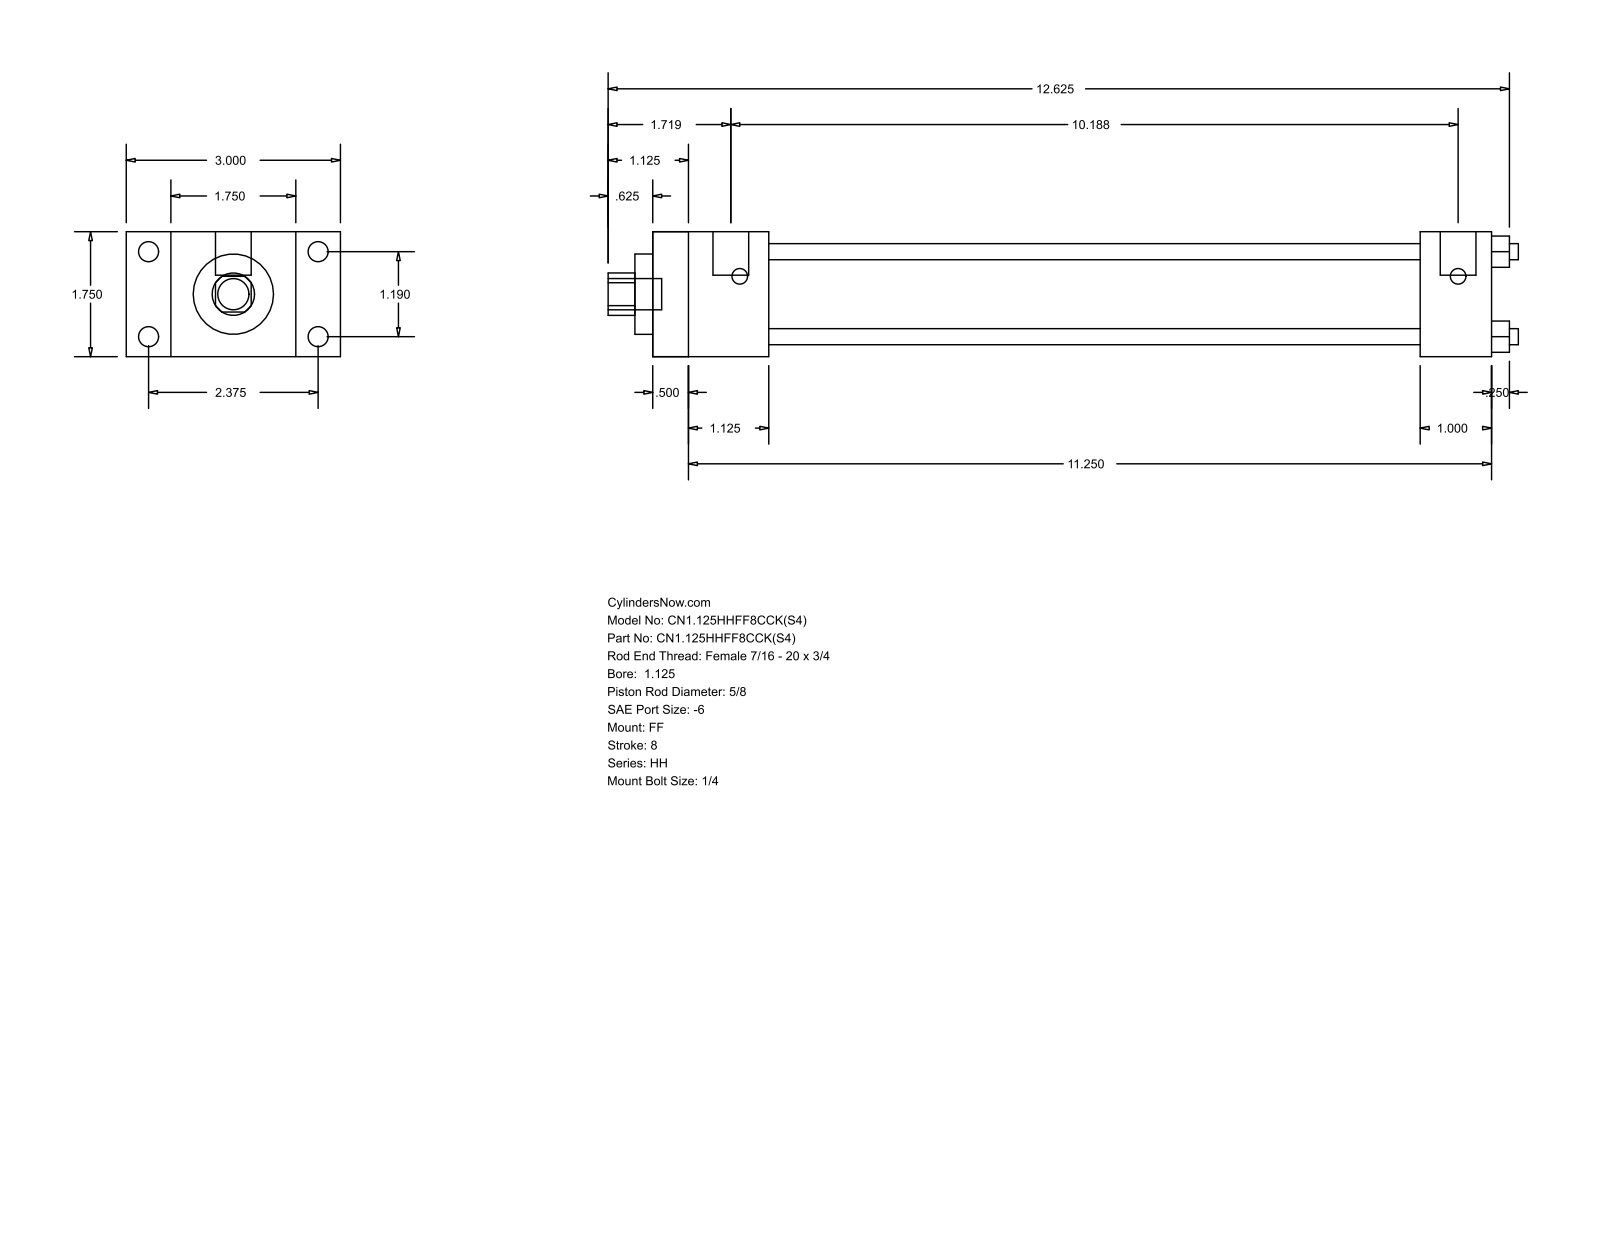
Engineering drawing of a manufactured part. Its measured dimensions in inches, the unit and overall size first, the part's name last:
Units: inches
Overall size (bounding box): 12.75 × 3 × 1.75
Round holes (diameter × count): ⌀0.225 ×4, ⌀0.625 ×1, ⌀1.125 ×1, ⌀1.375 ×1
Round bosses / shafts (diameter × count): ⌀0.281 ×4, ⌀0.219 ×4, ⌀0.5 ×2, ⌀0.437 ×1
Partial cylindrical surfaces — rounded edges, fillets, slot ends (radius × count): R0.297 ×1
Main face-to-face distances: 1.75, 11.75, 0.5, 11.25, 0.625, 2.375, 1.125, 1.625, 10.75, 10.25
Hole centre spacings: 0.841, 1.19, 1.683
Bodies: 0 solids, 92 faces (64 planar, 28 cylindrical, 0 other)
Part name (STEP PRODUCT): HH_FF__0112_0.625
STEP written by: GSSL Pune (CONFIG_CONTROL_DESIGN)
